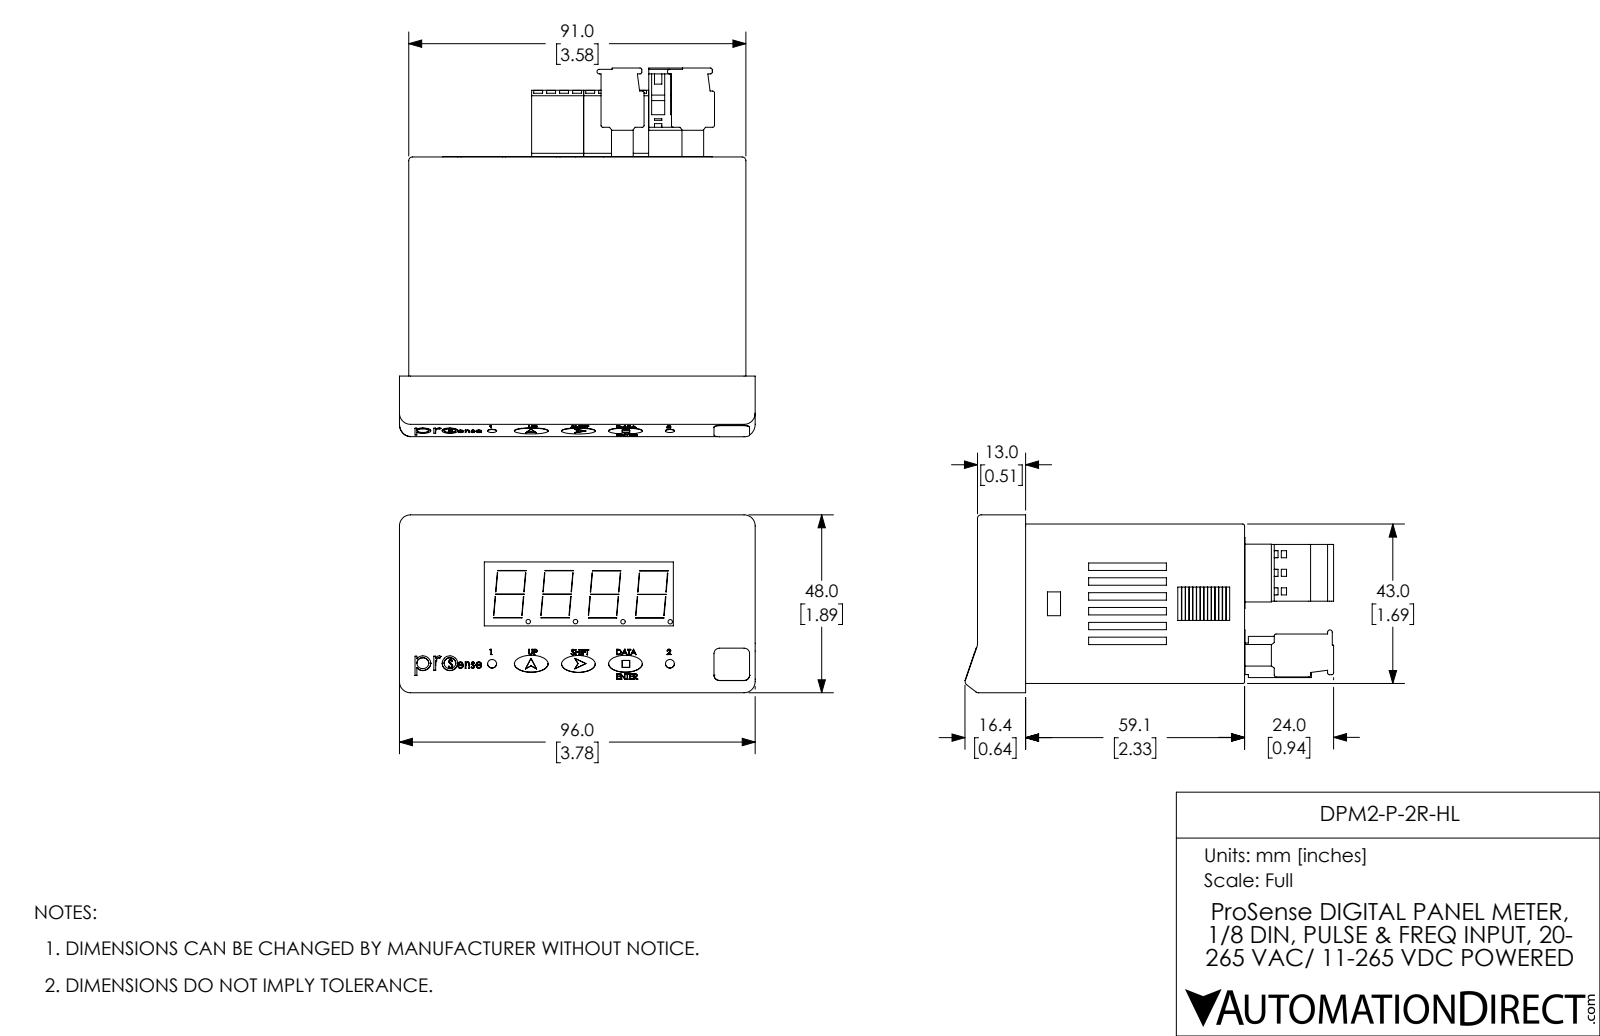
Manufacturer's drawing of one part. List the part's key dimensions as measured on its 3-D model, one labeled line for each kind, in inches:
Part name (STEP PRODUCT): DPM2-P Coord fXT
STEP written by: SolidWorks 2017 (AUTOMOTIVE_DESIGN)
Units: inches
Bodies: 10 solids, 1974 faces (1519 planar, 293 cylindrical, 162 other)
Overall size (bounding box): 3.916 × 3.78 × 1.89
Volume: 5.392 in³ · Surface area: 99.79 in²
Round holes (diameter × count): ⌀0.039 ×9, ⌀0.079 ×9, ⌀0.078 ×8, ⌀0.118 ×8, ⌀0.152 ×8
Round bosses / shafts (diameter × count): ⌀0.047 ×4, ⌀0.095 ×2
Partial cylindrical surfaces — rounded edges, fillets, slot ends (radius × count): R0.004 ×53, R0.012 ×18, R0.014 ×18, R0.02 ×17, R0.118 ×10, R0.039 ×9, R0.07 ×9, R0.072 ×9
Main face-to-face distances: 0.059, 1.634, 0.098, 1.693, 1.575, 1.732, 0.157, 0.433, 3.524, 2.78
Hole centre spacings: 0.138, 0.197, 0.201, 0.748, 0.276, 0.197, 0.201, 0.398
